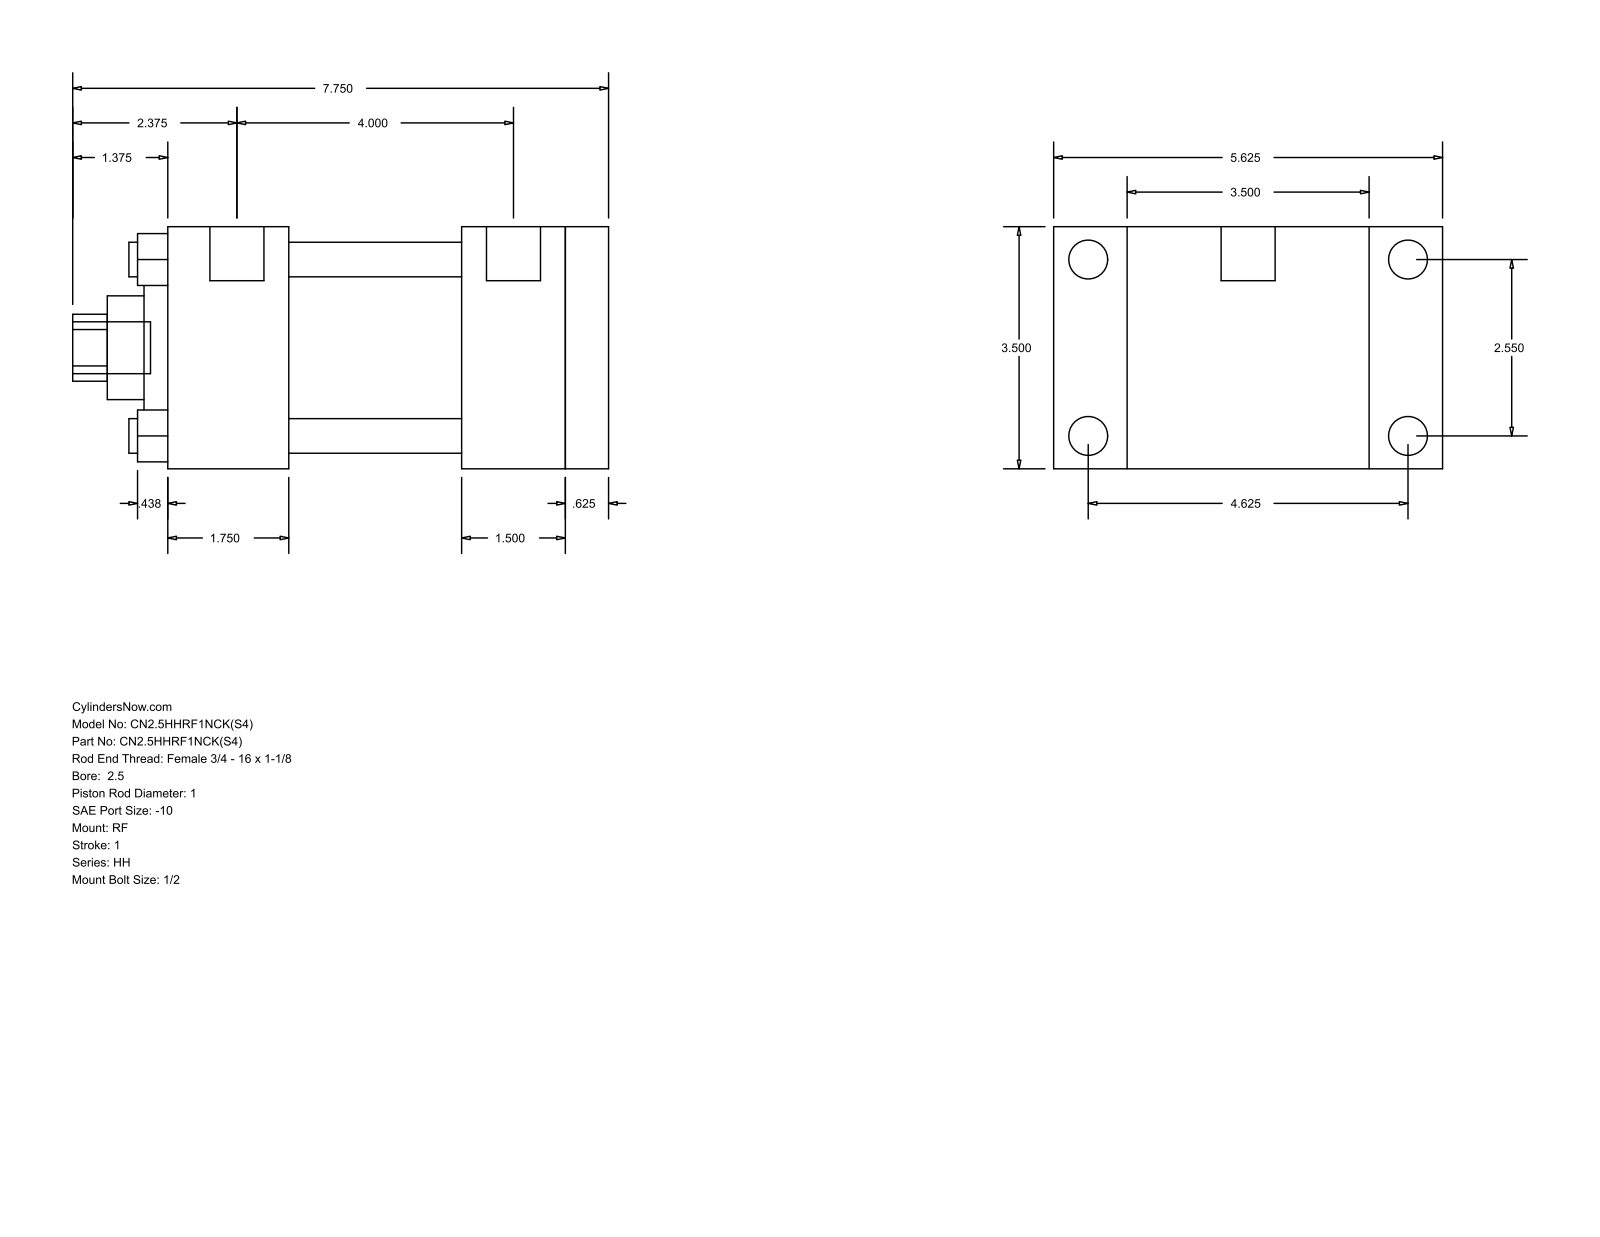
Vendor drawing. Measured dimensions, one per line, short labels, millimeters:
name: HH_RF__0250_1
written by: GSSL Pune (CONFIG_CONTROL_DESIGN)
unit: mm
bodies: 0 solids, 94 faces (65 planar, 29 cylindrical, 0 other)
size: 196.85 × 142.88 × 88.9
holes: 4× ⌀12.7, 1× ⌀25.4, 1× ⌀38.1, 1× ⌀60.33, 1× ⌀73.03
bosses: 4× ⌀14.3, 4× ⌀5.56, 2× ⌀19.84, 1× ⌀19.05
rounds: 1× R12.29
face distances: 88.9, 15.88, 146.05, 161.93, 44.46, 101.59, 117.47, 107.96, 63.5, 38.09
hole spacings: 45.79, 64.76, 91.58
